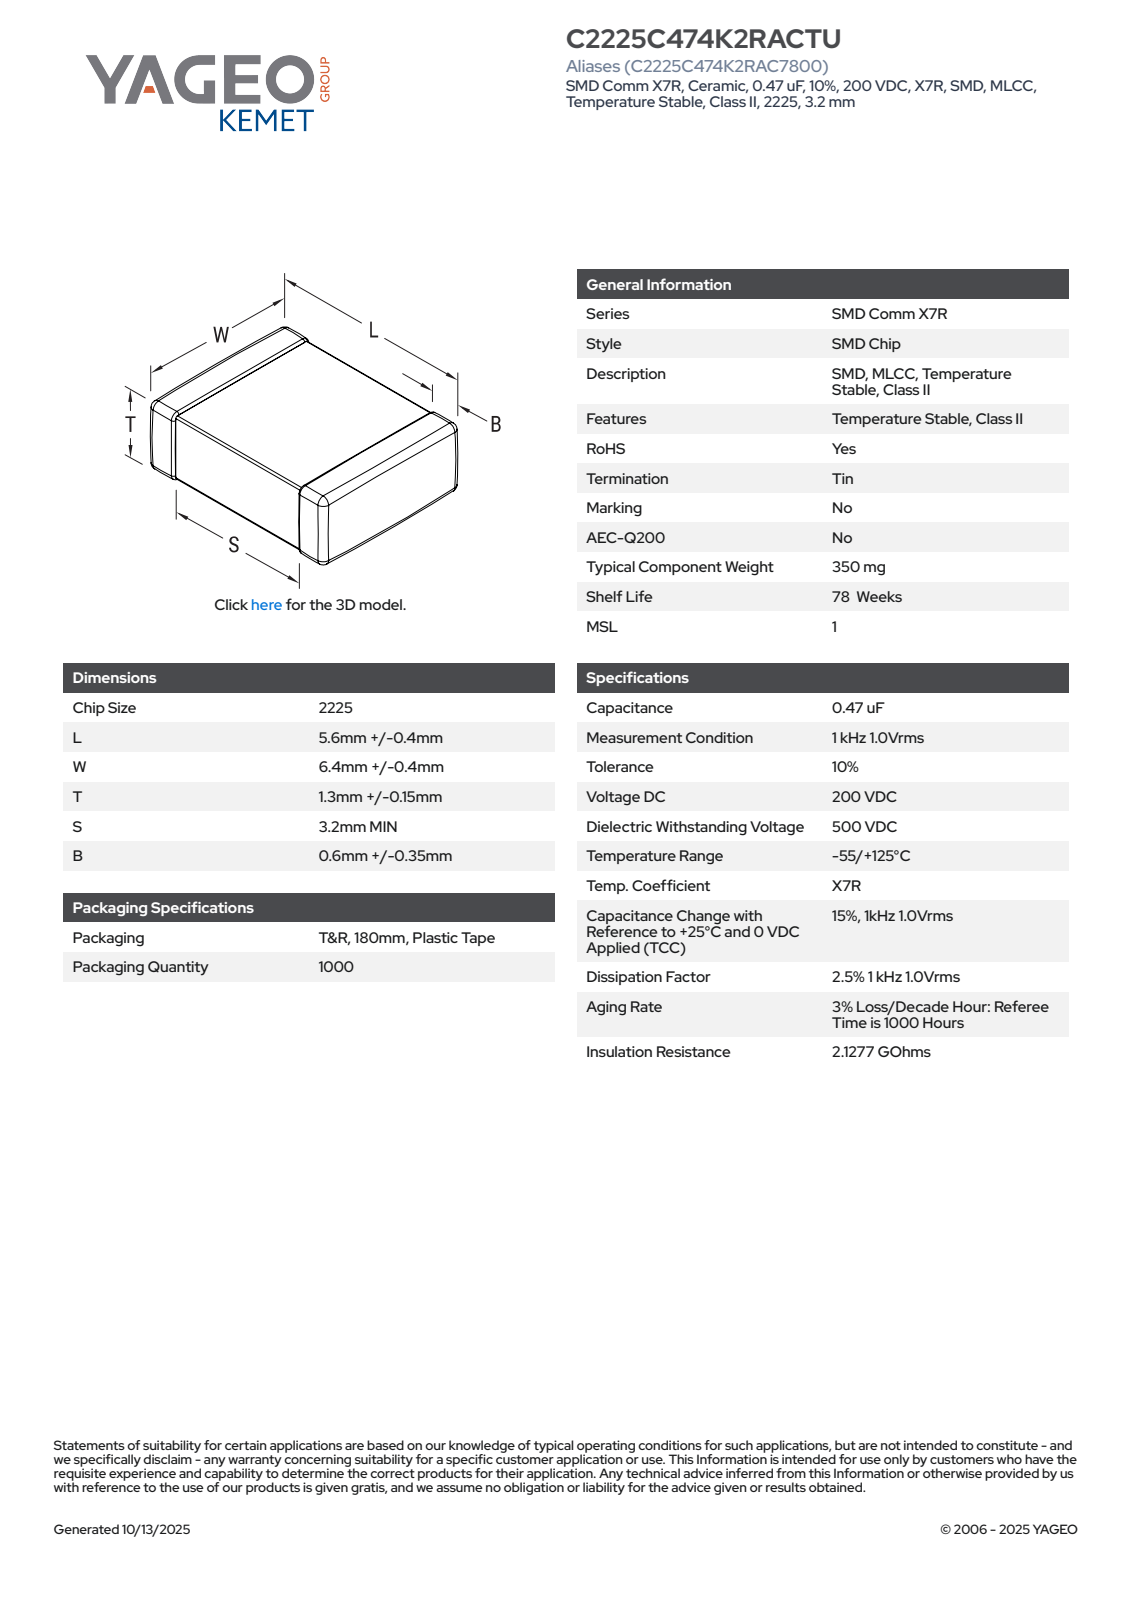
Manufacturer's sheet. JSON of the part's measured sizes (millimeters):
{"part_name": "CCS_CCSTD_2225_L6W6.8T1.45B0.6", "step_written_by": "SolidWorks 2021 (AUTOMOTIVE_DESIGN)", "units": "millimeters", "bodies": {"solids": 4, "faces": 125, "planar": 71, "cylindrical": 38, "other": 16}, "overall_size": [6.8, 6, 1.45], "volume_mm3": 50, "surface_area_mm2": 119, "partial_cylinders_radius": [[0.14, 24]], "face_to_face_distances": [1.17, 1.31, 1.45, 6, 6.52, 6.66, 6.8, 1, 2.24, 3.76]}
